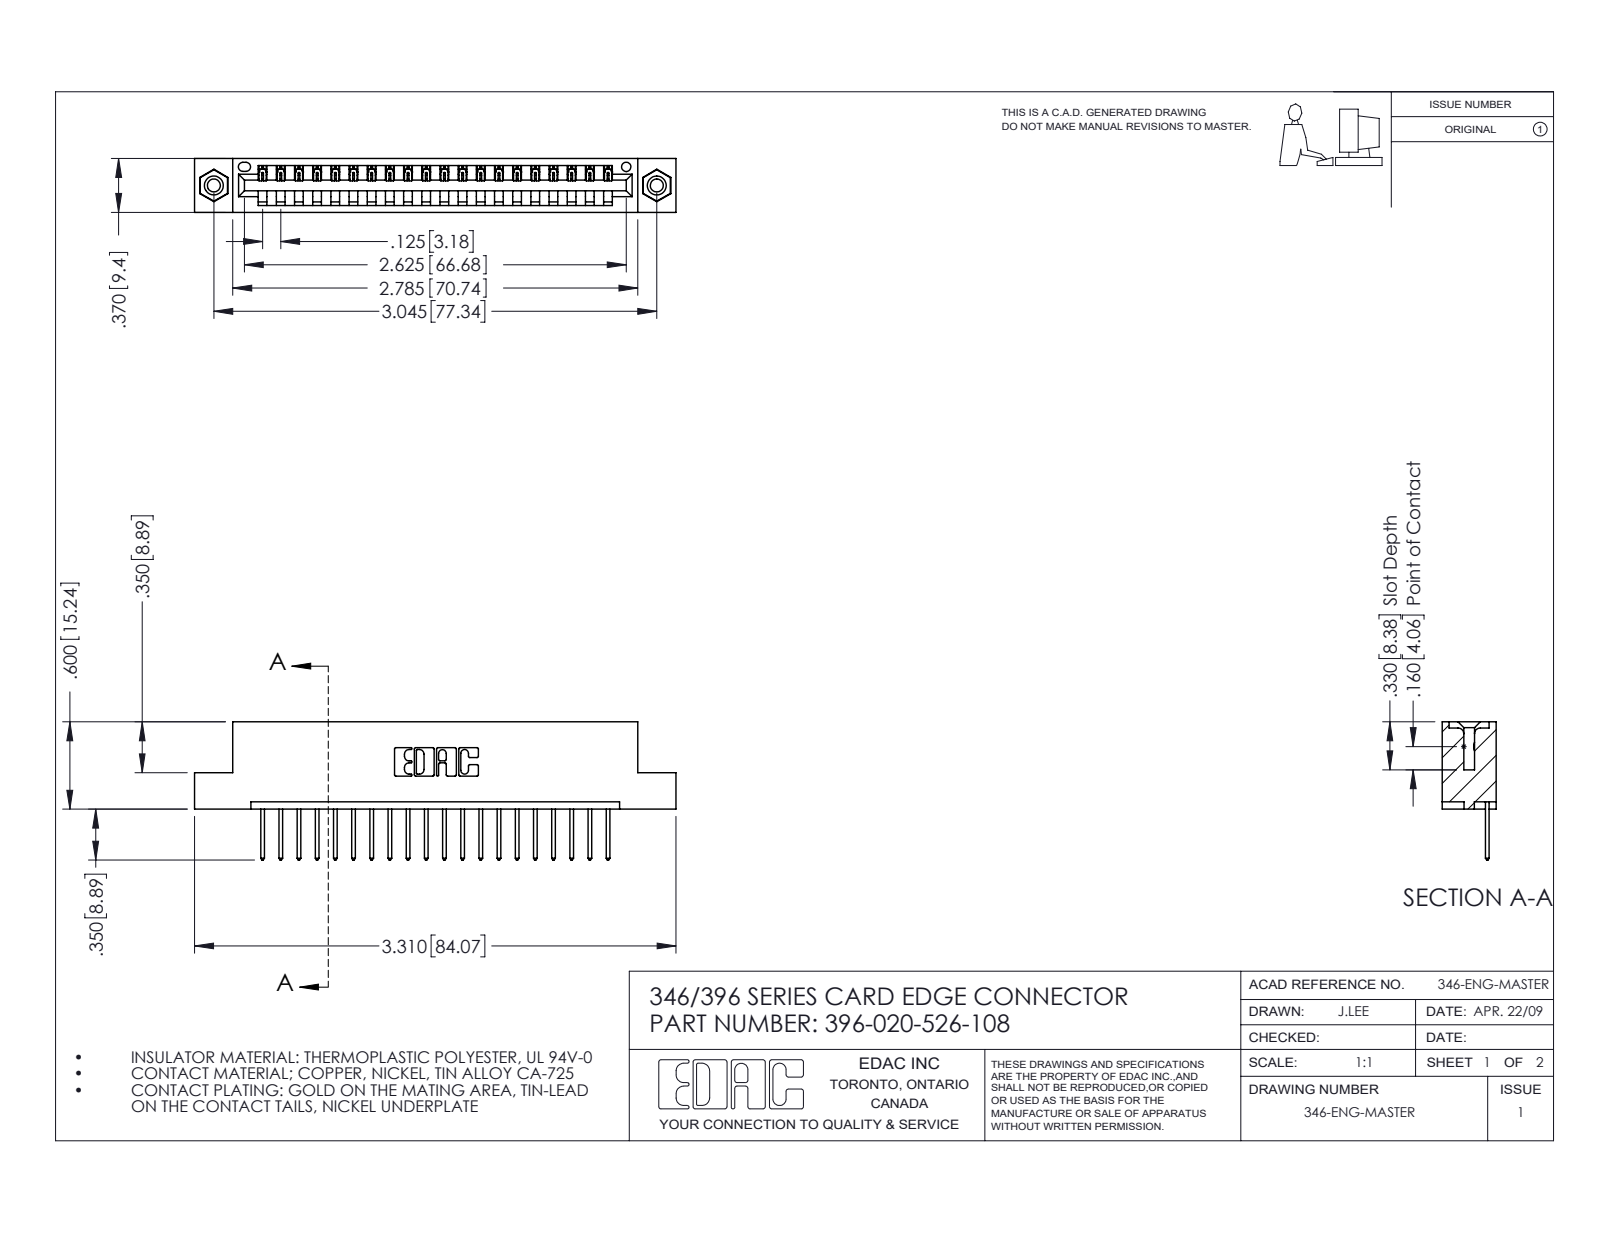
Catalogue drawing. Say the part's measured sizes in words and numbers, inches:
The part is named "345-250-001_345-250-003-102; 346 Part_Flush Mounting Lugs - 0.156 Dia-TI; 345-292-001_345-293-126; 396-020-526-108". Its 3-D file was written by "SolidWorks 2016 (CONFIG_CONTROL_DESIGN)". It is 23 solids with 1342 faces: 908 planar, 418 cylindrical and 16 other. Overall it measures 3.31 by 0.95 by 0.37 inches. Its volume is 0.48 cubic inches and its surface area 14.89 square inches. Round holes: 2 of diameter 0.089, 2 of diameter 0.125, 2 of diameter 0.156, 1 of diameter 0.064. Round bosses or shafts: 2 of diameter 0.155. Partial cylindrical surfaces (rounded edges, fillets, slot ends): 40 of radius 0.006, 40 of radius 0.01, 22 of radius 0.01, 6 of radius 0.007, 6 of radius 0.031, 3 of radius 0.026, 2 of radius 0.031, 2 of radius 0.04. The main face-to-face distances are 0.048, 0.322, 0.25, 0.37, 0.072, 0.298, 0.025, 0.148, 0.222, 0.1. The hole center spacings are 0.246, 2.837, 3.045.
